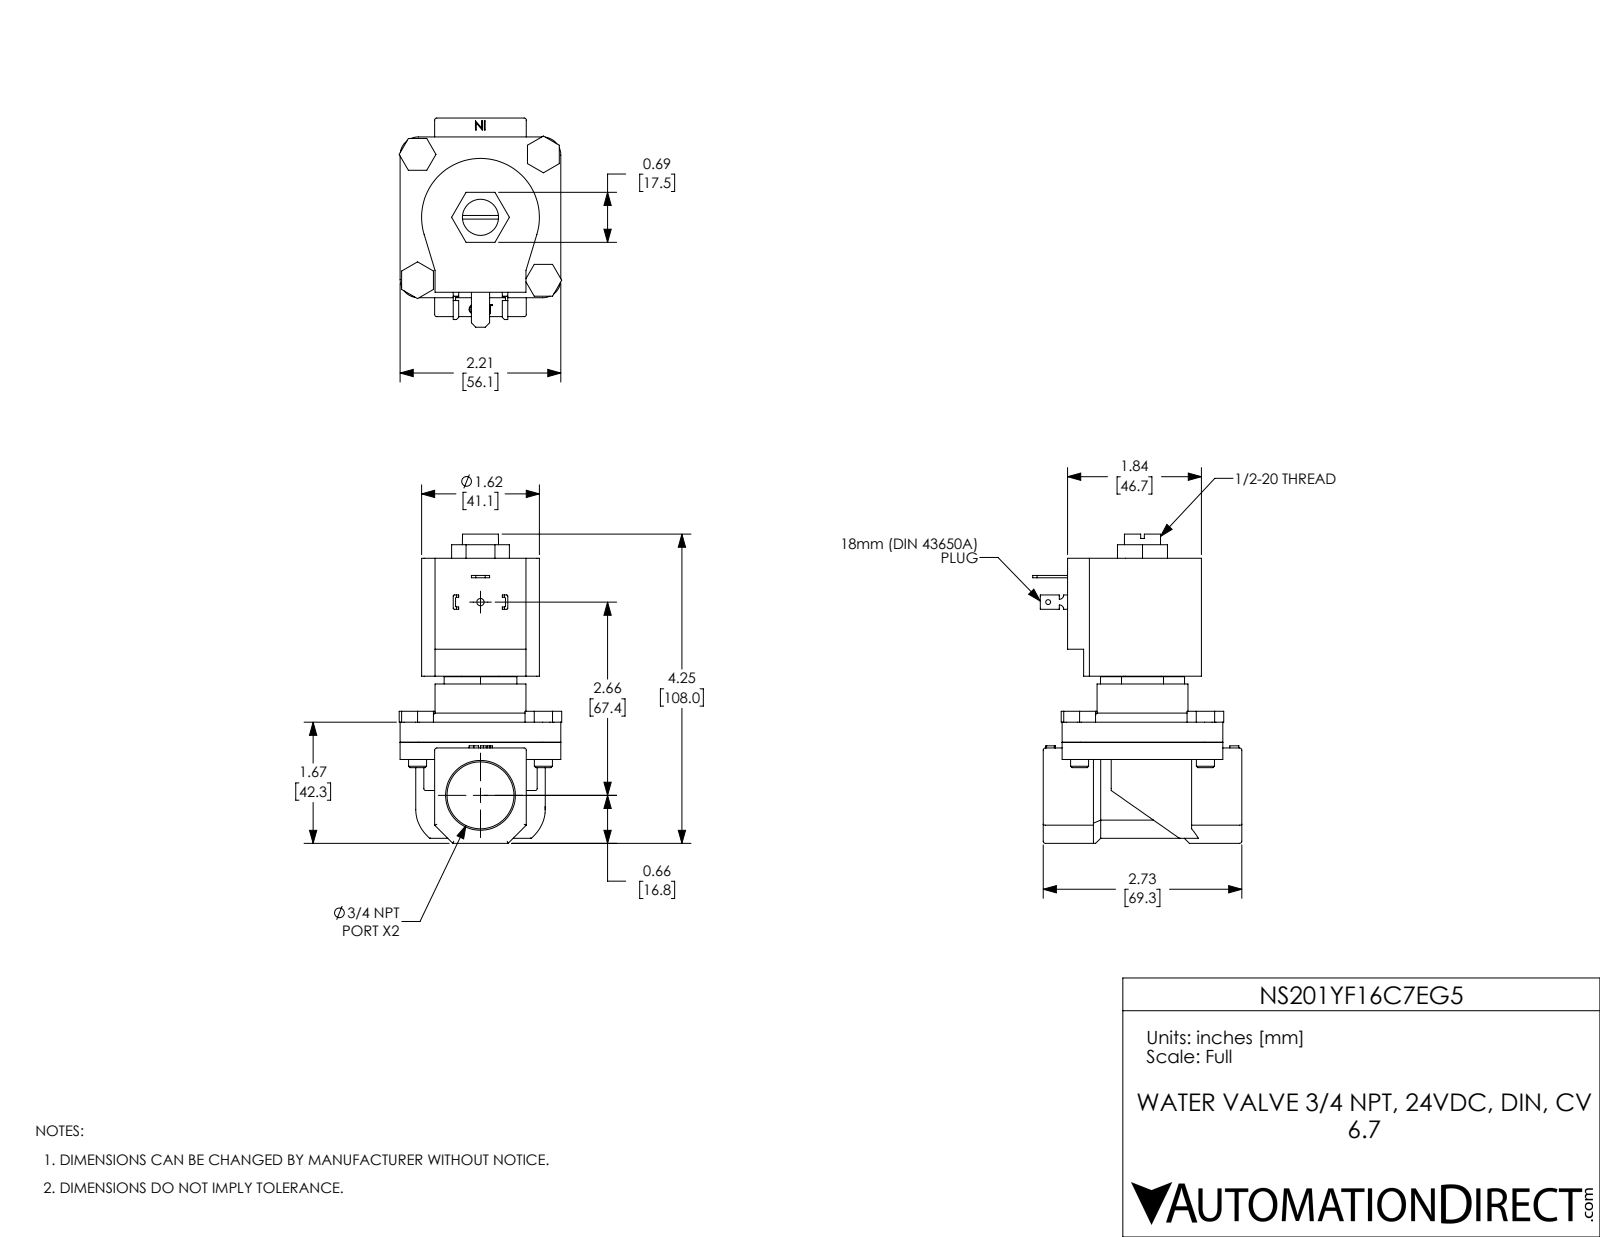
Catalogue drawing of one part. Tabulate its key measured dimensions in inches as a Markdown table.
| quantity | value |
| --- | --- |
| part name | NS201YF16C7EG5 |
| STEP written by | SolidWorks 2021 (CONFIG_CONTROL_DESIGN) |
| units | inches |
| bodies | 11 solids, 332 faces (198 planar, 99 cylindrical, 35 other) |
| overall size | 4.25 × 2.875 × 2.235 |
| volume | 10.35 in³ |
| surface area | 67.29 in² |
| round holes (diameter × count) | 0.25 × 4, 0.067 × 1, 0.1 × 1, 0.496 × 1, 0.512 × 1, 0.92 × 1, 1.155 × 1 |
| round bosses / shafts (diameter × count) | 0.248 × 4, 1.25 × 1 |
| partial cylindrical surfaces (radius × count) | 0.03 × 15, 0.015 × 8, 0.25 × 4, 0.06 × 2, 0.81 × 1, 0.89 × 1 |
| main face-to-face distances | 0.276, 2.529, 2.253, 0.475, 1.735, 2.21, 0.236, 0.512, 2.765, 0.26 |
| hole center spacings | 1.223, 1.73, 2.446, 2.656 |
